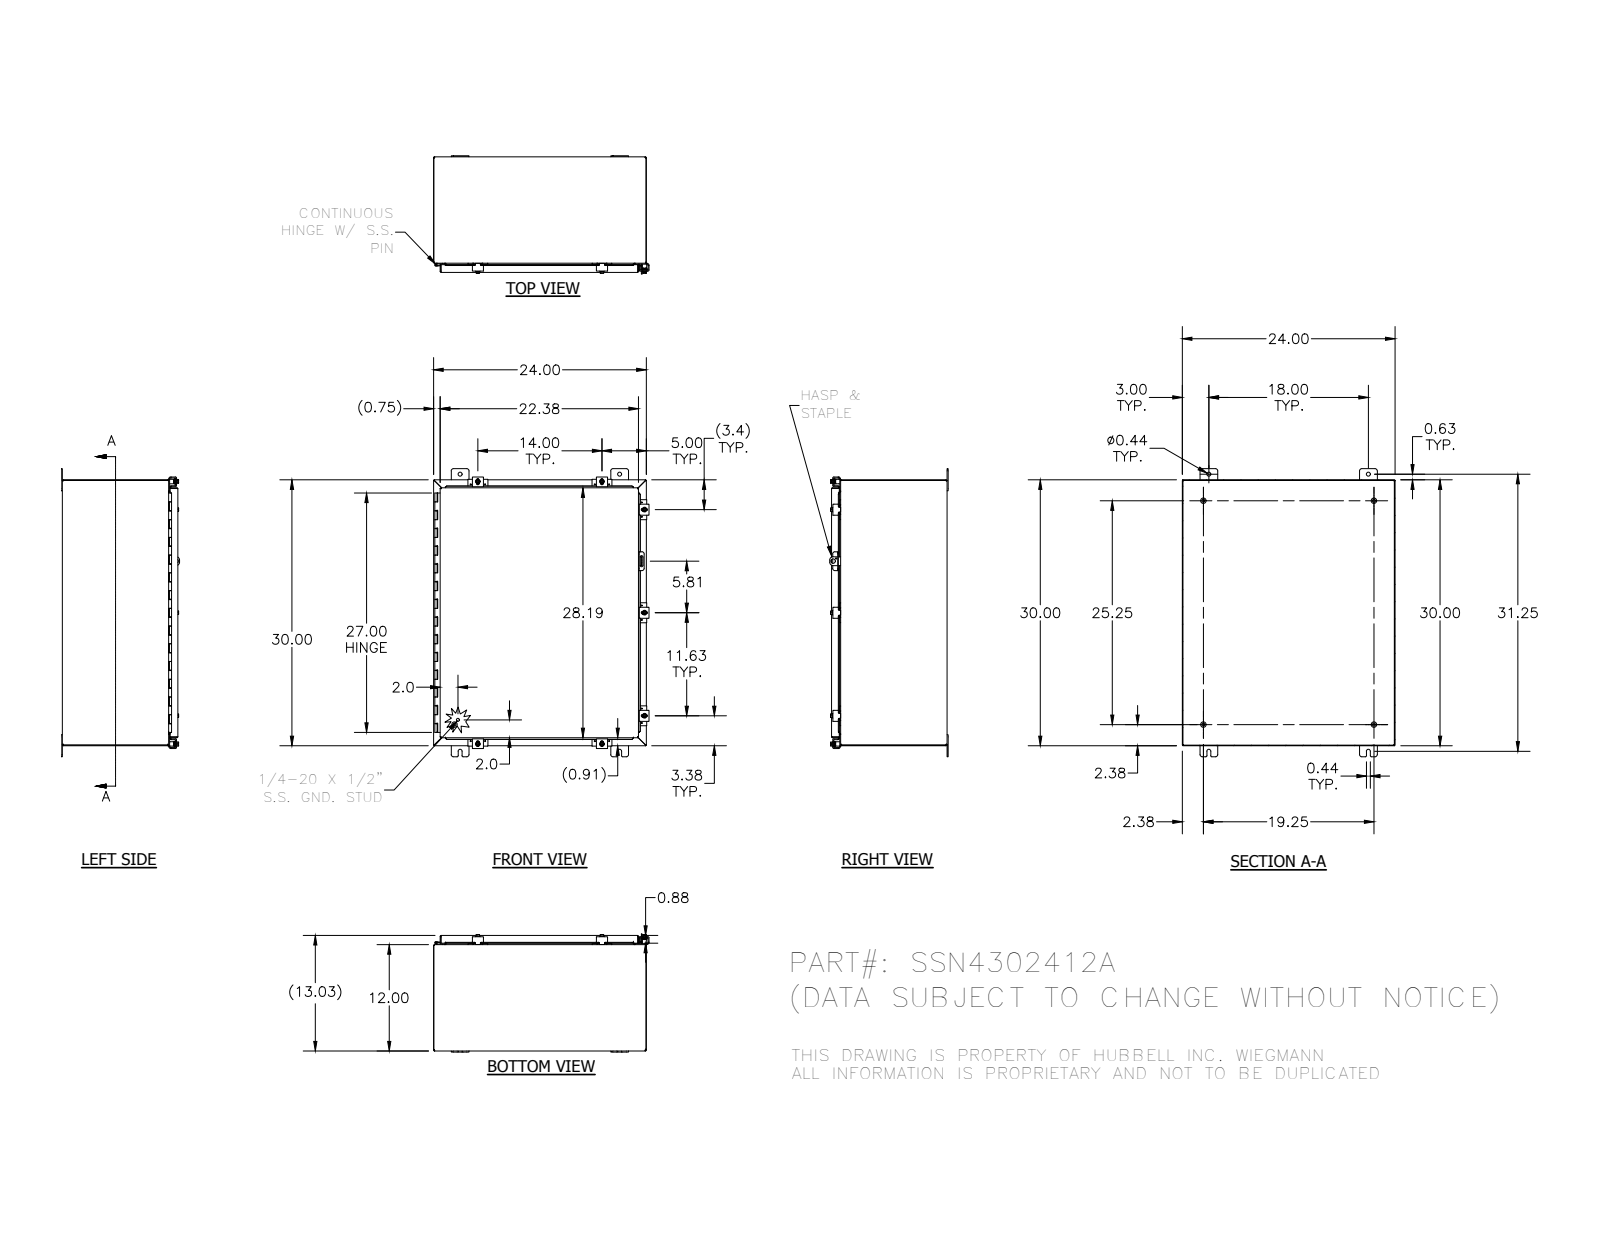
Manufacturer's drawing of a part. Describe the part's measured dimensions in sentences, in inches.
The part is named "28x22; 34871; 30824-3; 38412 (+8 more)". Its 3-D file was written by "SolidWorks 2014 (AUTOMOTIVE_DESIGN)". It is 52 solids with 2090 faces: 818 planar, 905 cylindrical and 367 other. Overall it measures 32.5 by 24.216 by 13.355 inches. Its volume is 239.6 cubic inches and its surface area 6 325 square inches. Round holes: 14 of diameter 0.11, 7 of diameter 0.211, 7 of diameter 0.281, 7 of diameter 0.3, 4 of diameter 0.438, 1 of diameter 0.125, 1 of diameter 0.156, 1 of diameter 0.5. Round bosses or shafts: 9 of diameter 0.25, 7 of diameter 0.52, 7 of diameter 0.5, 7 of diameter 0.35, 4 of diameter 0.625, 4 of diameter 0.33, 1 of diameter 0.337, 1 of diameter 0.12. Partial cylindrical surfaces (rounded edges, fillets, slot ends): 83 of radius 0.03, 37 of radius 0.125, 33 of radius 0.25, 23 of radius 0.031, 23 of radius 0.105, 18 of radius 0.062, 14 of radius 0.141, 10 of radius 0.1. The main face-to-face distances are 0.074, 12.959, 23.926, 12.885, 13.033, 29.926, 23.852, 24, 30, 29.852. The hole center spacings are 0.876, 29.3, 14, 1.625, 13.191, 14.816, 28.961, 29.006.
